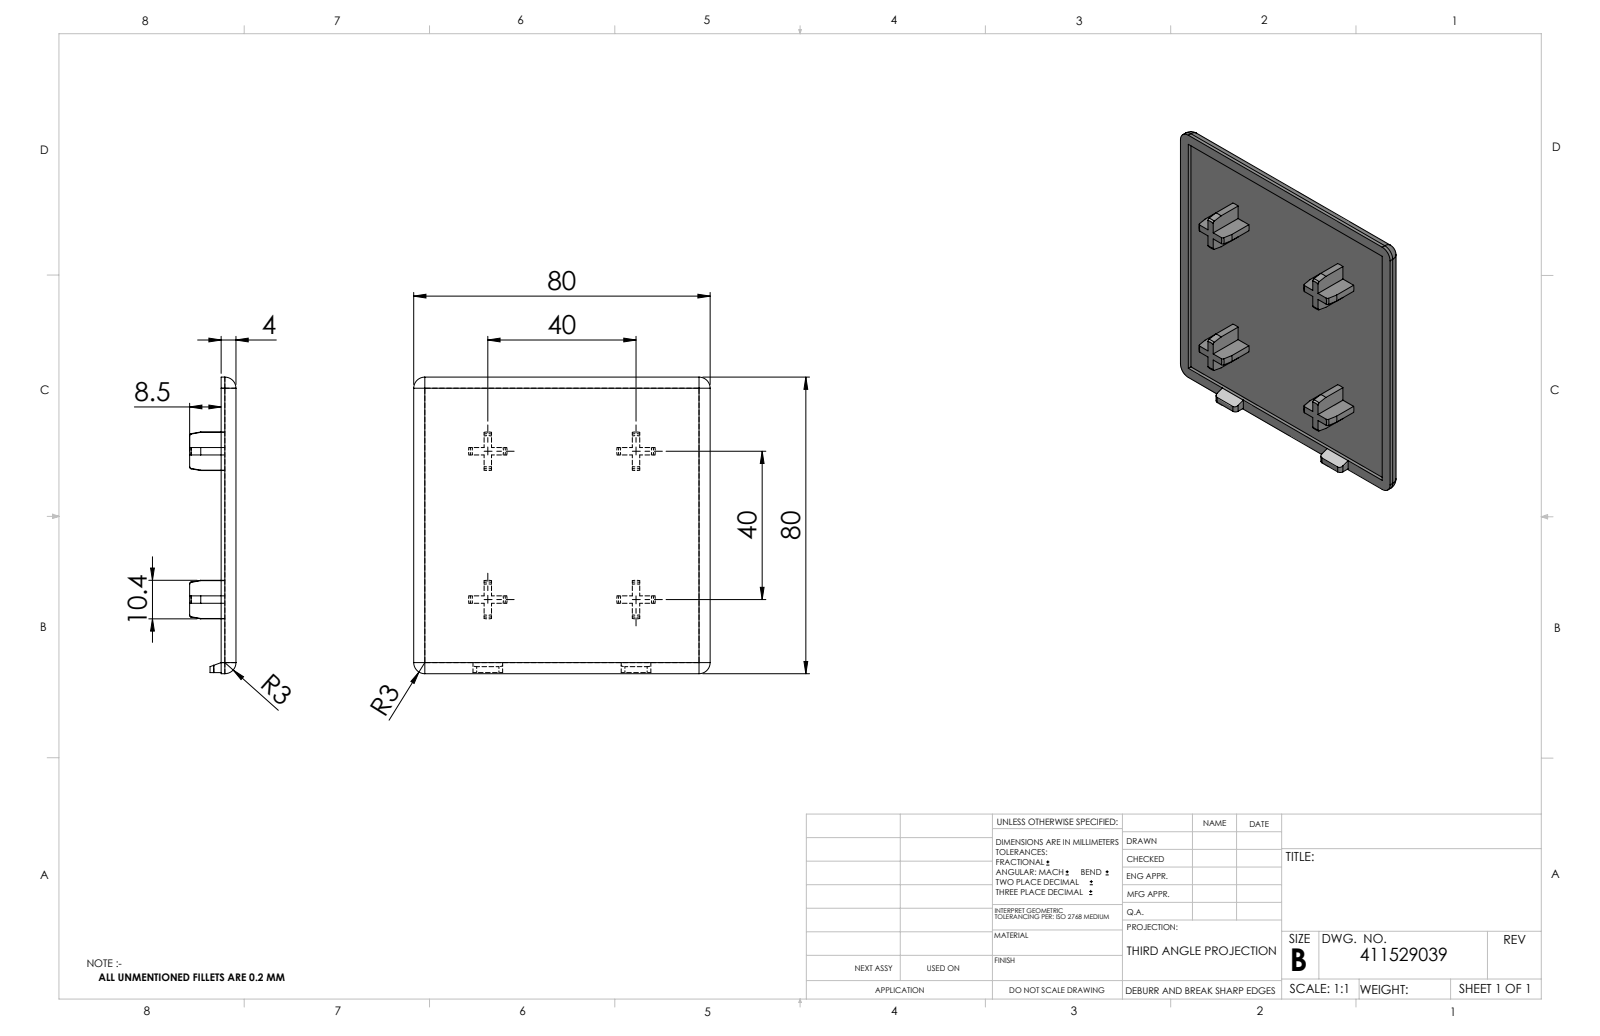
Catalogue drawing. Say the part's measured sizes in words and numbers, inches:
The part is named "411529039". Its 3-D file was written by "SolidWorks 2014 (CONFIG_CONTROL_DESIGN)". It is 1 solid with 137 faces: 57 planar, 32 cylindrical and 48 other. Overall it measures 3.15 by 3.15 by 0.492 inches. Its volume is 1.281 cubic inches and its surface area 24.09 square inches. Partial cylindrical surfaces (rounded edges, fillets, slot ends): 8 of radius 0.118, 4 of radius 0.039, 4 of radius 0.205. The main face-to-face distances are 0.118, 0.157, 0.039, 1.575, 0.079, 0.827, 2.402, 0.63, 2.205, 1.654.
